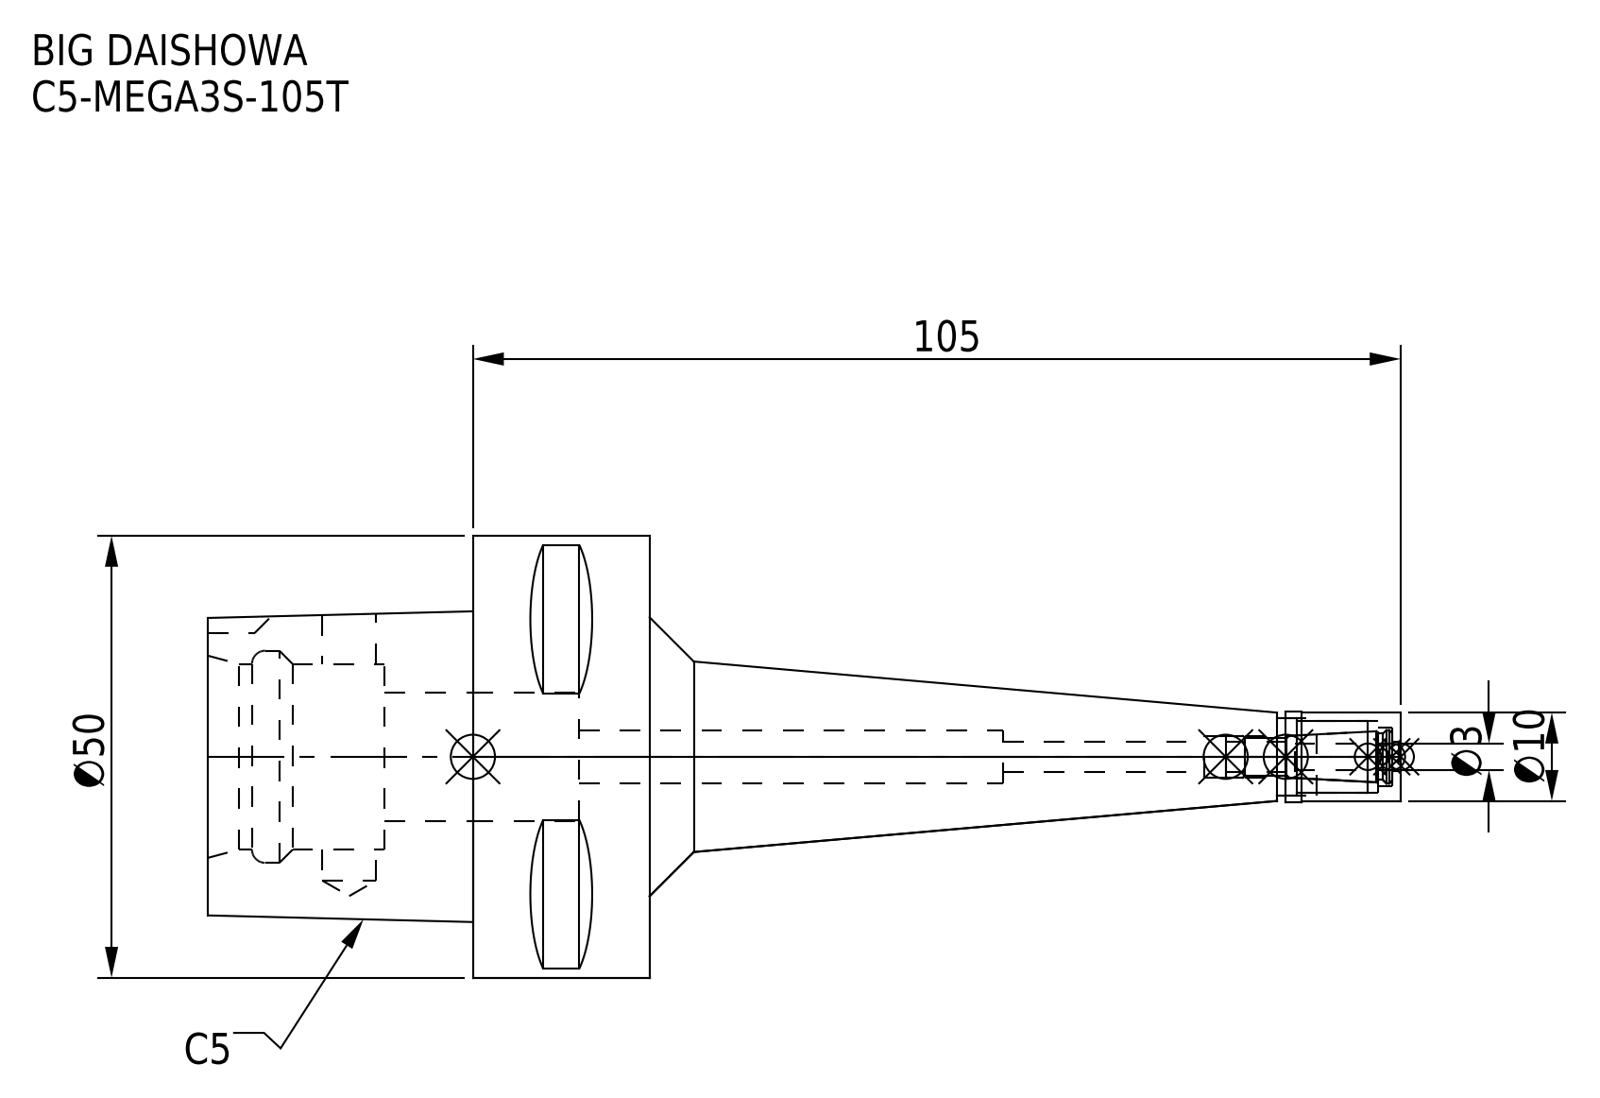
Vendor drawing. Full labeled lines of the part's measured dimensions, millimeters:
Part name (STEP PRODUCT): C5-MEGA3S-105T-030-FreeParts; C5-MEGA3S-105T-030_ASM.stp; MGN3S_1.stp; DXF_TEMP_ASSY_ASM_4_ASM.stp (+3 more)
STEP written by: SolidWorks 2019 (CONFIG_CONTROL_DESIGN)
Units: millimetres
Bodies: 2 solids, 93 faces (38 planar, 37 cylindrical, 18 other)
Overall size (bounding box): 135 × 50 × 50
Volume: 69 800 mm³ · Surface area: 18 695 mm²
Round holes (diameter × count): ⌀3.3 ×1, ⌀3.4 ×1, ⌀4.7 ×1, ⌀6 ×1, ⌀6.1 ×1, ⌀6.6 ×1, ⌀8.2 ×1, ⌀8.7 ×1, ⌀14.5 ×1, ⌀21 ×1, ⌀24 ×1
Round bosses / shafts (diameter × count): ⌀50 ×1, ⌀10.3 ×1, ⌀10 ×1
Partial cylindrical surfaces — rounded edges, fillets, slot ends (radius × count): R4 ×1
Main face-to-face distances: 20, 30, 50, 44, 10, 12, 19.18, 8, 22, 42
